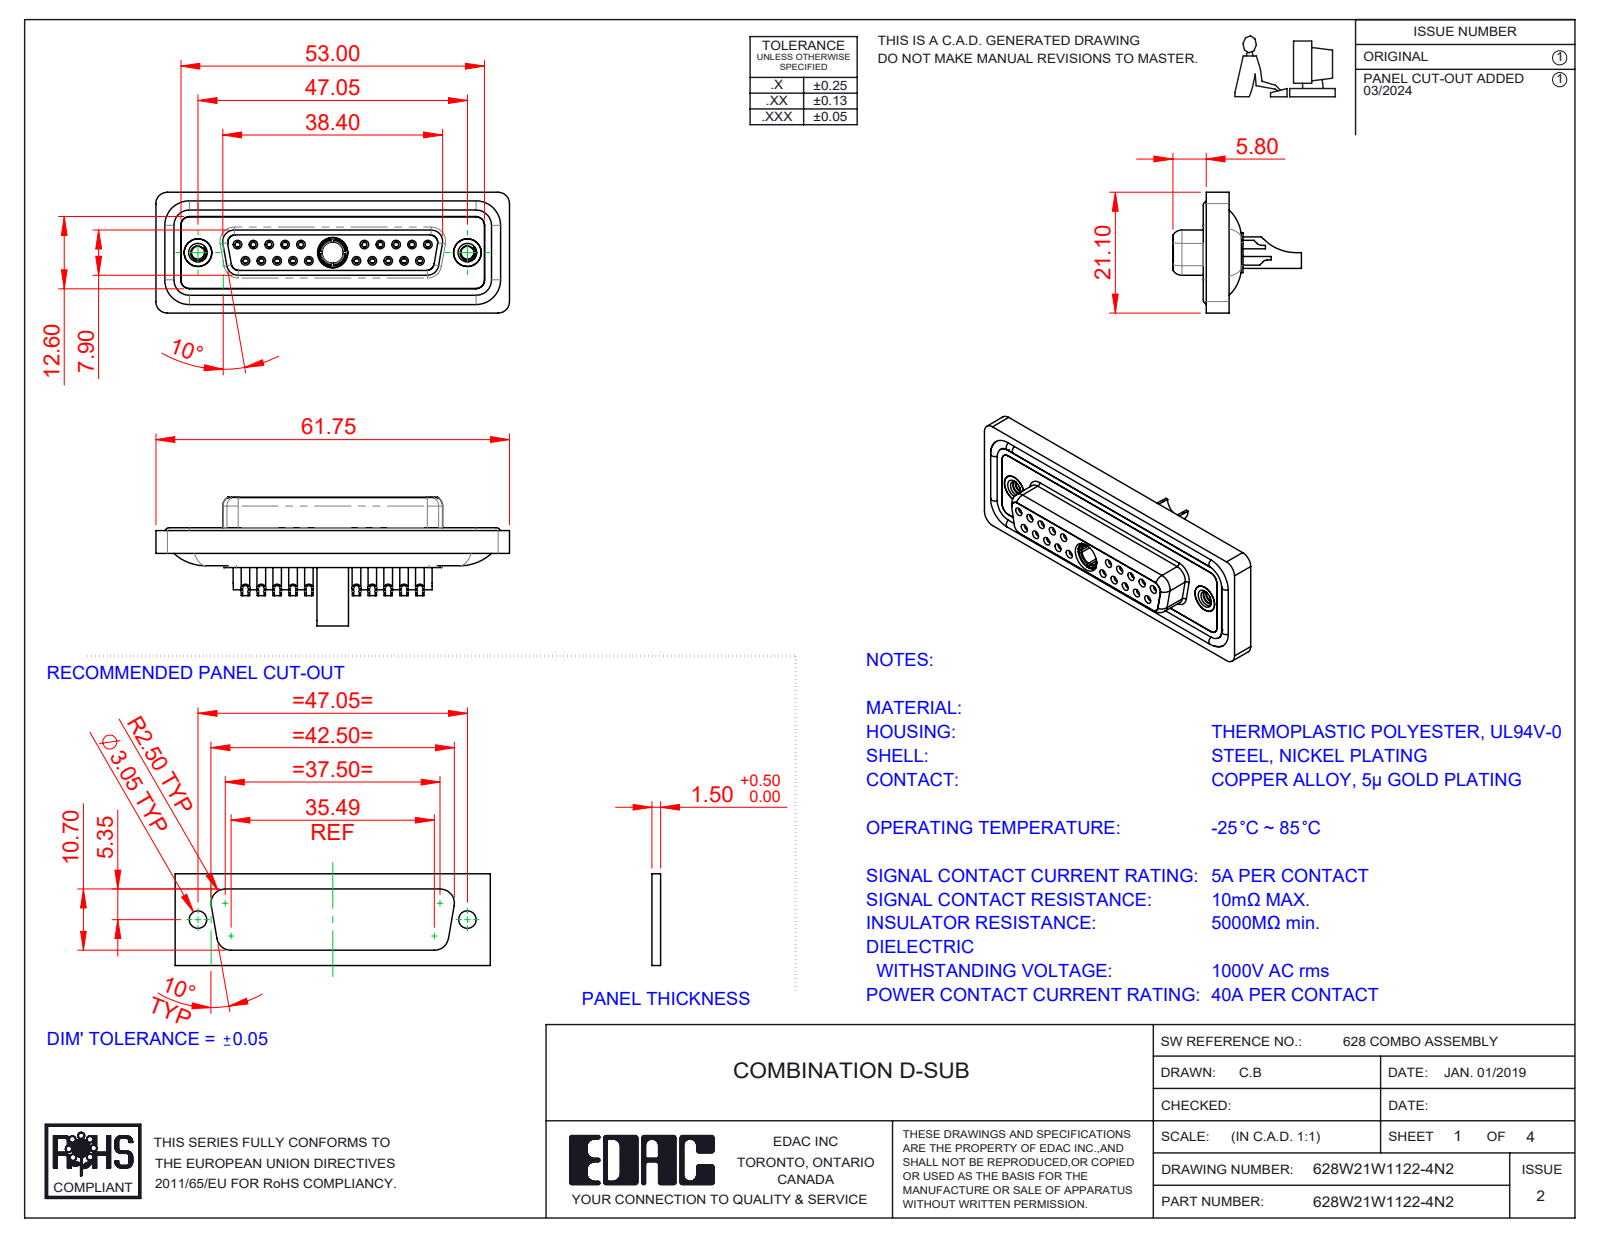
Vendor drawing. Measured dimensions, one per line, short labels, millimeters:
name: 628Combo Contact Row 1_22; Power Socket_40A SC; 628Combo Shell Front_25 Contacts; 628Combo Shell Rear_25 Contacts (+5 more)
written by: SolidWorks 2023 (CONFIG_CONTROL_DESIGN)
unit: mm
bodies: 29 solids, 1563 faces (476 planar, 632 cylindrical, 455 other)
size: 61.75 × 22.45 × 21.1
volume: 8 455 mm³; area: 14 352 mm²
holes: 20× ⌀0.9, 20× ⌀1, 20× ⌀1.1, 20× ⌀1.5, 20× ⌀2, 10× ⌀1.6, 10× ⌀1.7, 3× ⌀4.85, 2× ⌀2.26, 2× ⌀4, 2× ⌀4.05, 2× ⌀5
bosses: 20× ⌀2.2, 14× ⌀1.6, 2× ⌀4.95, 2× ⌀4.8, 1× ⌀5.5, 1× ⌀5.2, 1× ⌀4.96, 1× ⌀4.75
rounds: 22× R1.5, 18× R2, 8× R1.35, 8× R1.6, 6× R1, 4× R0.25, 4× R0.5, 4× R0.6
face distances: 0.4, 1.8, 7.45, 5.65, 6.6, 0.5, 1.6, 7.05, 2.9, 1.1
hole spacings: 3.16, 2.77, 5.54, 5.03, 8.31, 7.48, 16.62, 19.39
